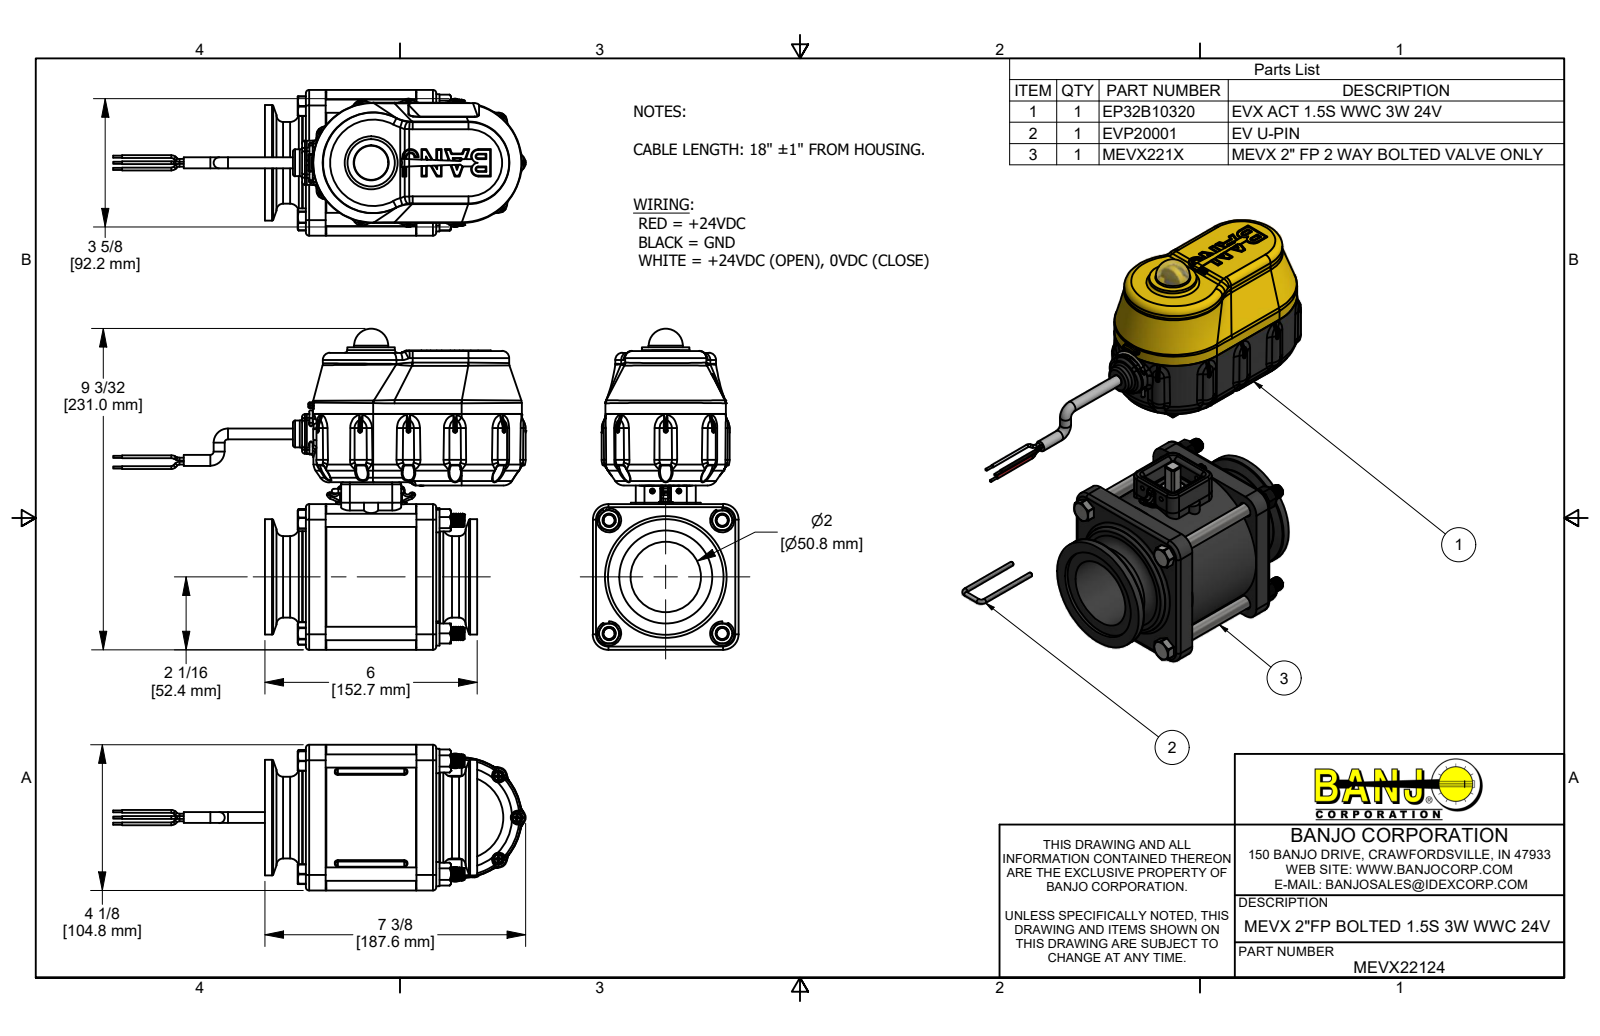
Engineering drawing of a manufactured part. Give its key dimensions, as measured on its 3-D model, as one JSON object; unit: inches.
{"part_name": "MEVX22124; EP32B10320; B61905PPHS; B632038PM (+8 more)", "step_written_by": "Autodesk Inventor 2019 (AUTOMOTIVE_DESIGN)", "units": "inches", "bodies": {"solids": 96, "faces": 11049, "planar": 2788, "cylindrical": 3331, "other": 4930}, "overall_size": [11.685, 9.095, 4.125], "volume_in3": 71.29, "surface_area_in2": 751.6, "round_holes": [[0.095, 11], [0.15, 11], [0.08, 7], [0.107, 4], [0.126, 4], [0.136, 4], [0.148, 4], [0.15, 4], [0.17, 4], [0.307, 4], [0.385, 4], [0.438, 4]], "round_bosses_or_shafts": [[0.324, 60], [0.25, 17], [0.08, 15], [0.14, 11], [0.108, 11], [0.085, 11], [0.058, 6], [0.375, 5]], "partial_cylinders_radius": [[0.013, 180], [0.04, 145], [0.01, 84], [0.02, 75], [0.005, 55], [0.03, 38], [0.08, 28], [0.06, 24]], "face_to_face_distances": [0.1, 2.565, 0.56, 3.13, 0.06, 0.211, 0.151, 0.72, 2.97, 0.16], "hole_center_spacings": [1.283, 2.265, 2.69, 2.715, 3.204, 1.662, 1.774, 2.458]}
